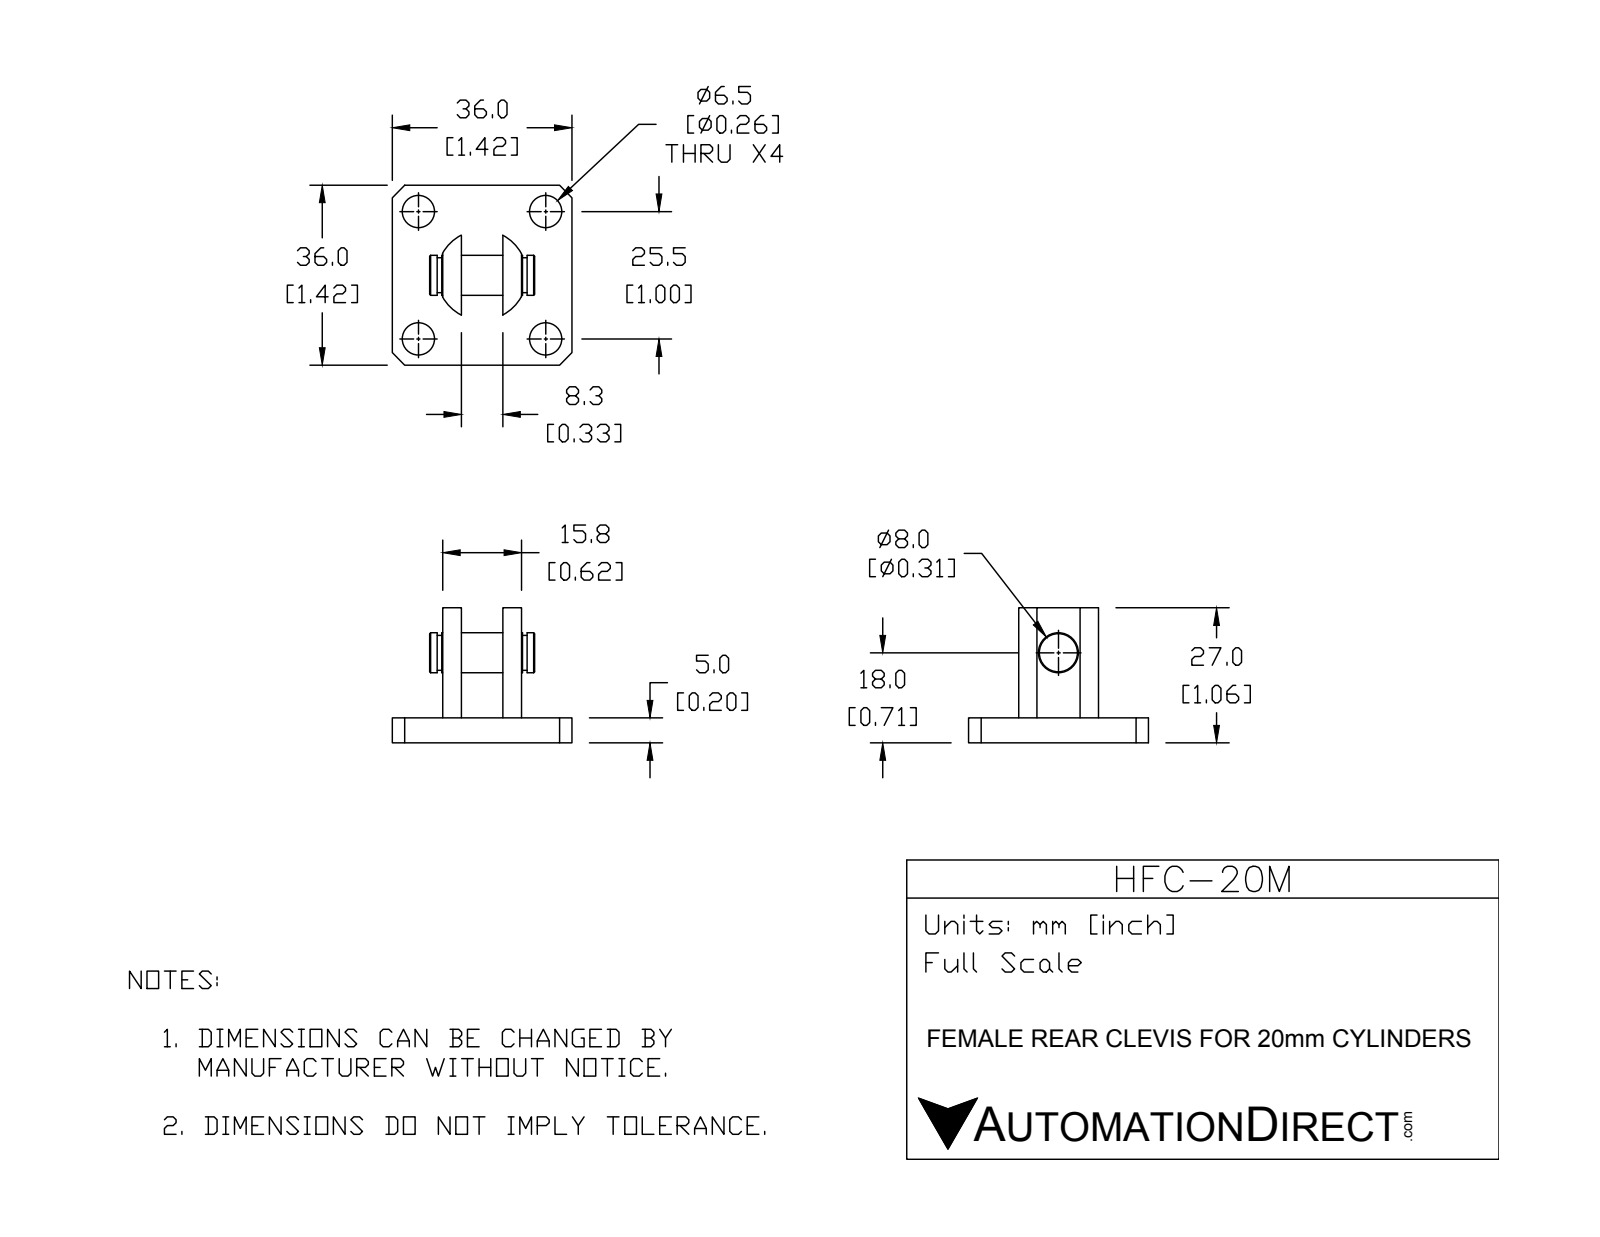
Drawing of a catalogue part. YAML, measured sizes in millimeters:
part_name: "HFC-20M"
step_written_by: "SolidWorks 2015 (CONFIG_CONTROL_DESIGN)"
units: millimeters
bodies: {solids: 2, faces: 52, planar: 22, cylindrical: 26, other: 4}
overall_size: [36, 36, 27]
volume: 8560
surface_area: 5603
round_holes:
  - {diameter: 6.5, count: 4}
round_bosses_or_shafts:
  - {diameter: 8, count: 1}
  - {diameter: 7, count: 1}
partial_cylinders:
  - {radius: 9, count: 1}
face_to_face_distances: [5, 36, 13.85, 22.15, 8.3, 10.1, 25.9, 3.75, 12.05, 15.8]
hole_center_spacings: [25.5, 36.06]
